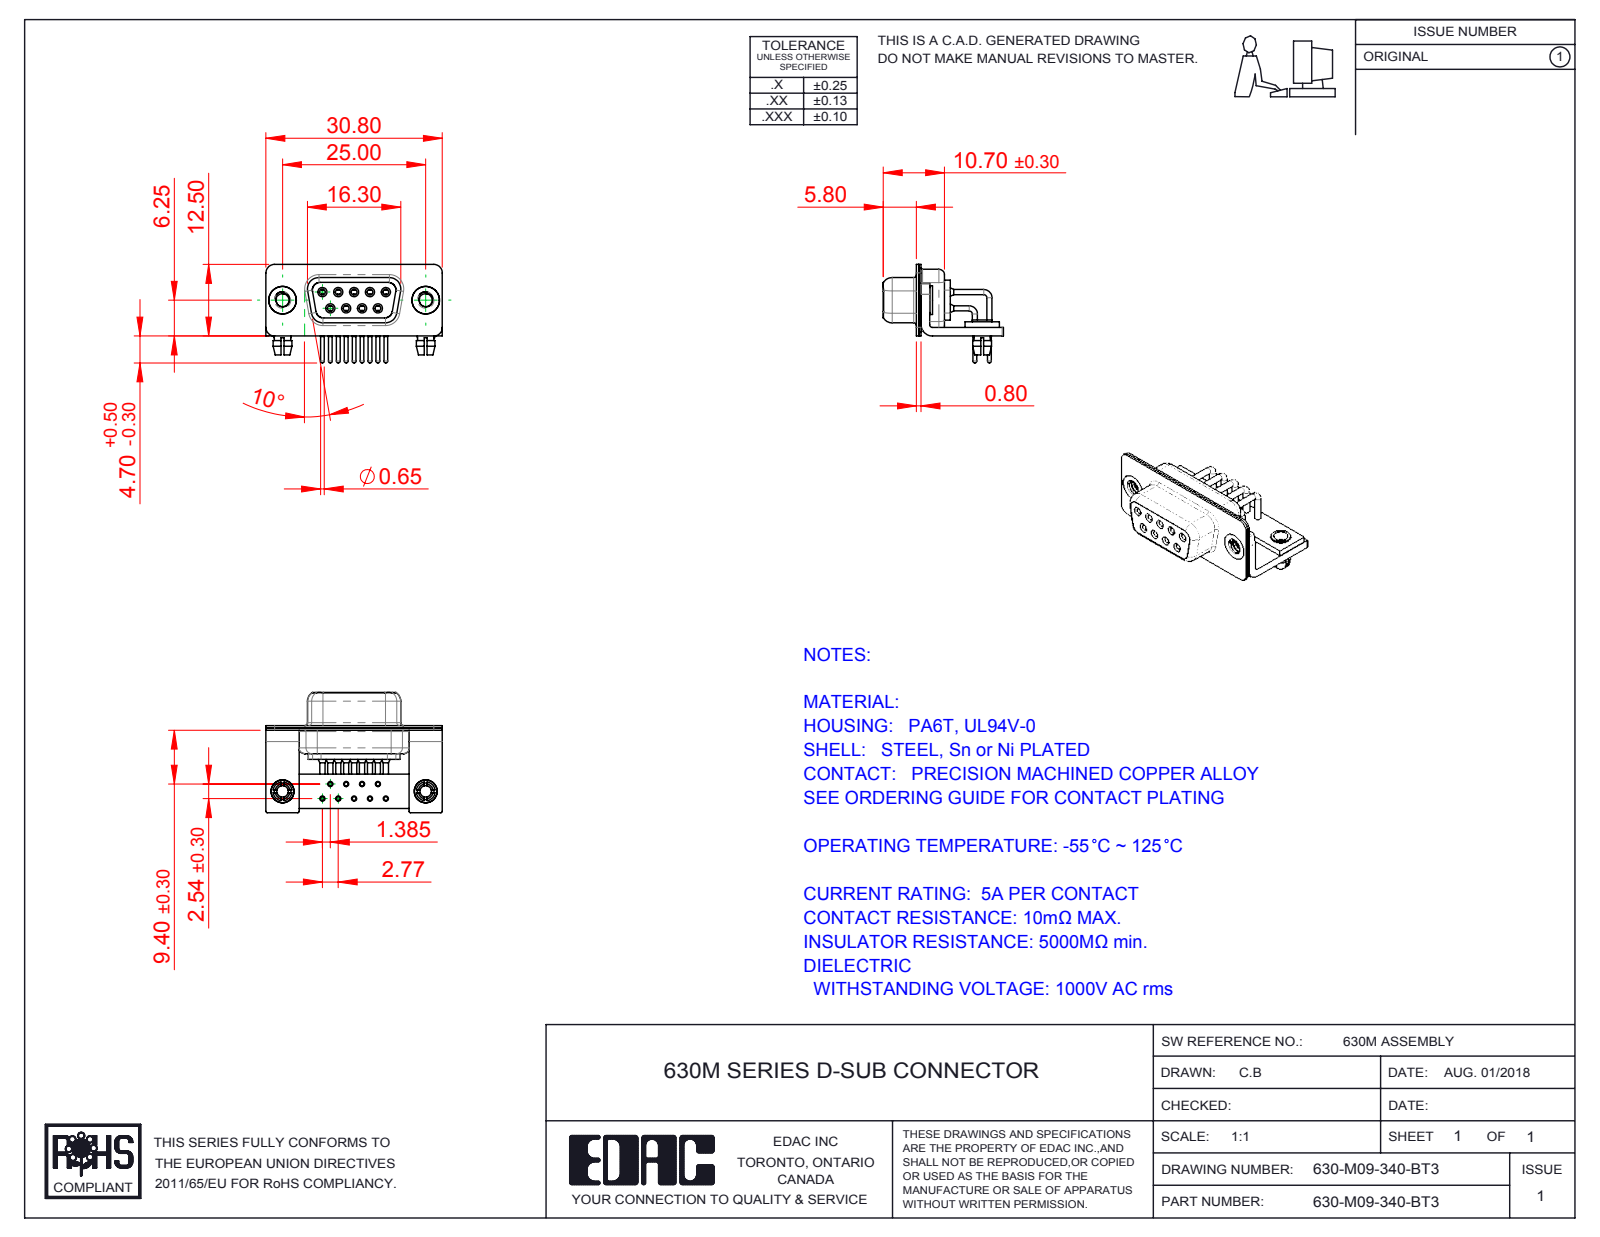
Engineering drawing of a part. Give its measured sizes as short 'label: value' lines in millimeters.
name: 630M Contact Row 1; 630M Board Lock; 630M Stabilizer Board_09 Contacts; 630M Shell Rear_09 Contacts (+6 more)
written by: SolidWorks 2016 (CONFIG_CONTROL_DESIGN)
unit: mm
bodies: 19 solids, 916 faces (276 planar, 416 cylindrical, 224 other)
size: 30.8 × 21 × 17.2
volume: 2 237 mm³; area: 5 917 mm²
holes: 11× ⌀2, 9× ⌀0.9, 9× ⌀1, 9× ⌀1.1, 9× ⌀1.7, 9× ⌀1.8, 2× ⌀2.26, 2× ⌀2.5, 2× ⌀3.2, 2× ⌀4, 2× ⌀4.8
bosses: 9× ⌀1.6, 9× ⌀1.5, 9× ⌀0.9, 9× ⌀0.65, 2× ⌀5, 2× ⌀4.9, 2× ⌀4, 2× ⌀3.4
rounds: 16× R0.25, 16× R1.5, 13× R2, 8× R1.35, 8× R1.6, 5× R0.5, 4× R0.6, 4× R0.65
face distances: 0.4, 0.8, 1.5, 2.3, 1.9, 1, 9.35, 1.45, 2.5, 8.95
hole spacings: 2.77, 5.54, 3.16, 4.87, 8.31, 2.89, 2.9, 5.03
